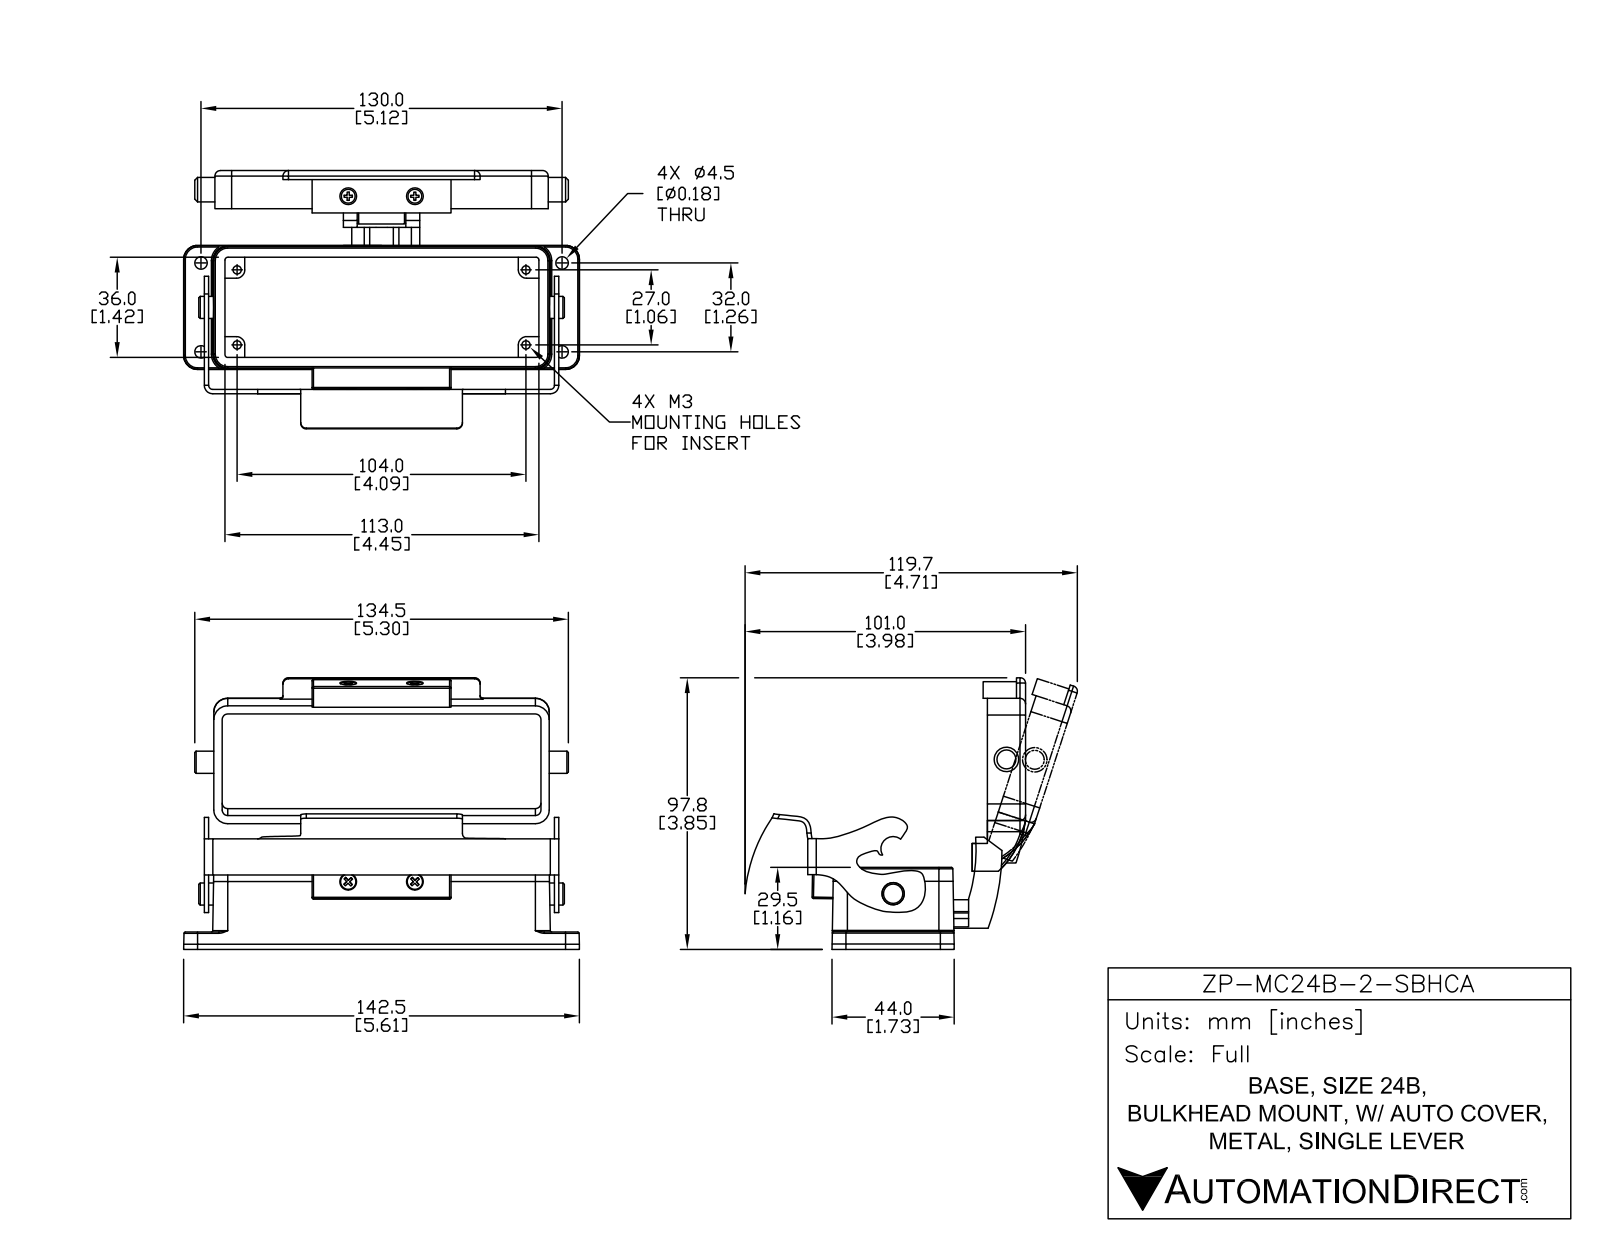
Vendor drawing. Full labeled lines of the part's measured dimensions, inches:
Part name (STEP PRODUCT): ZP-MC24B-2-SBHCA
STEP written by: SolidWorks 2014 (AUTOMOTIVE_DESIGN)
Units: inches
Bodies: 3 solids, 428 faces (191 planar, 143 cylindrical, 94 other)
Overall size (bounding box): 5.61 × 3.849 × 3.395
Volume: 5.887 in³ · Surface area: 91.54 in²
Round holes (diameter × count): ⌀0.128 ×4, ⌀0.173 ×4, ⌀0.079 ×1, ⌀0.315 ×1
Round bosses / shafts (diameter × count): ⌀0.315 ×1, ⌀0.313 ×1
Partial cylindrical surfaces — rounded edges, fillets, slot ends (radius × count): R0.02 ×29, R0.079 ×17, R0.118 ×8, R0.197 ×6, R0.041 ×4, R0.039 ×3, R0.059 ×2, R0.12 ×2
Main face-to-face distances: 0.118, 1.417, 0.061, 1.594, 1.871, 1.932, 0.454, 0.515, 0.222, 4.671
Hole centre spacings: 0.515, 1.274, 4.612, 4.757, 1.079, 1.26, 4.105, 4.244
